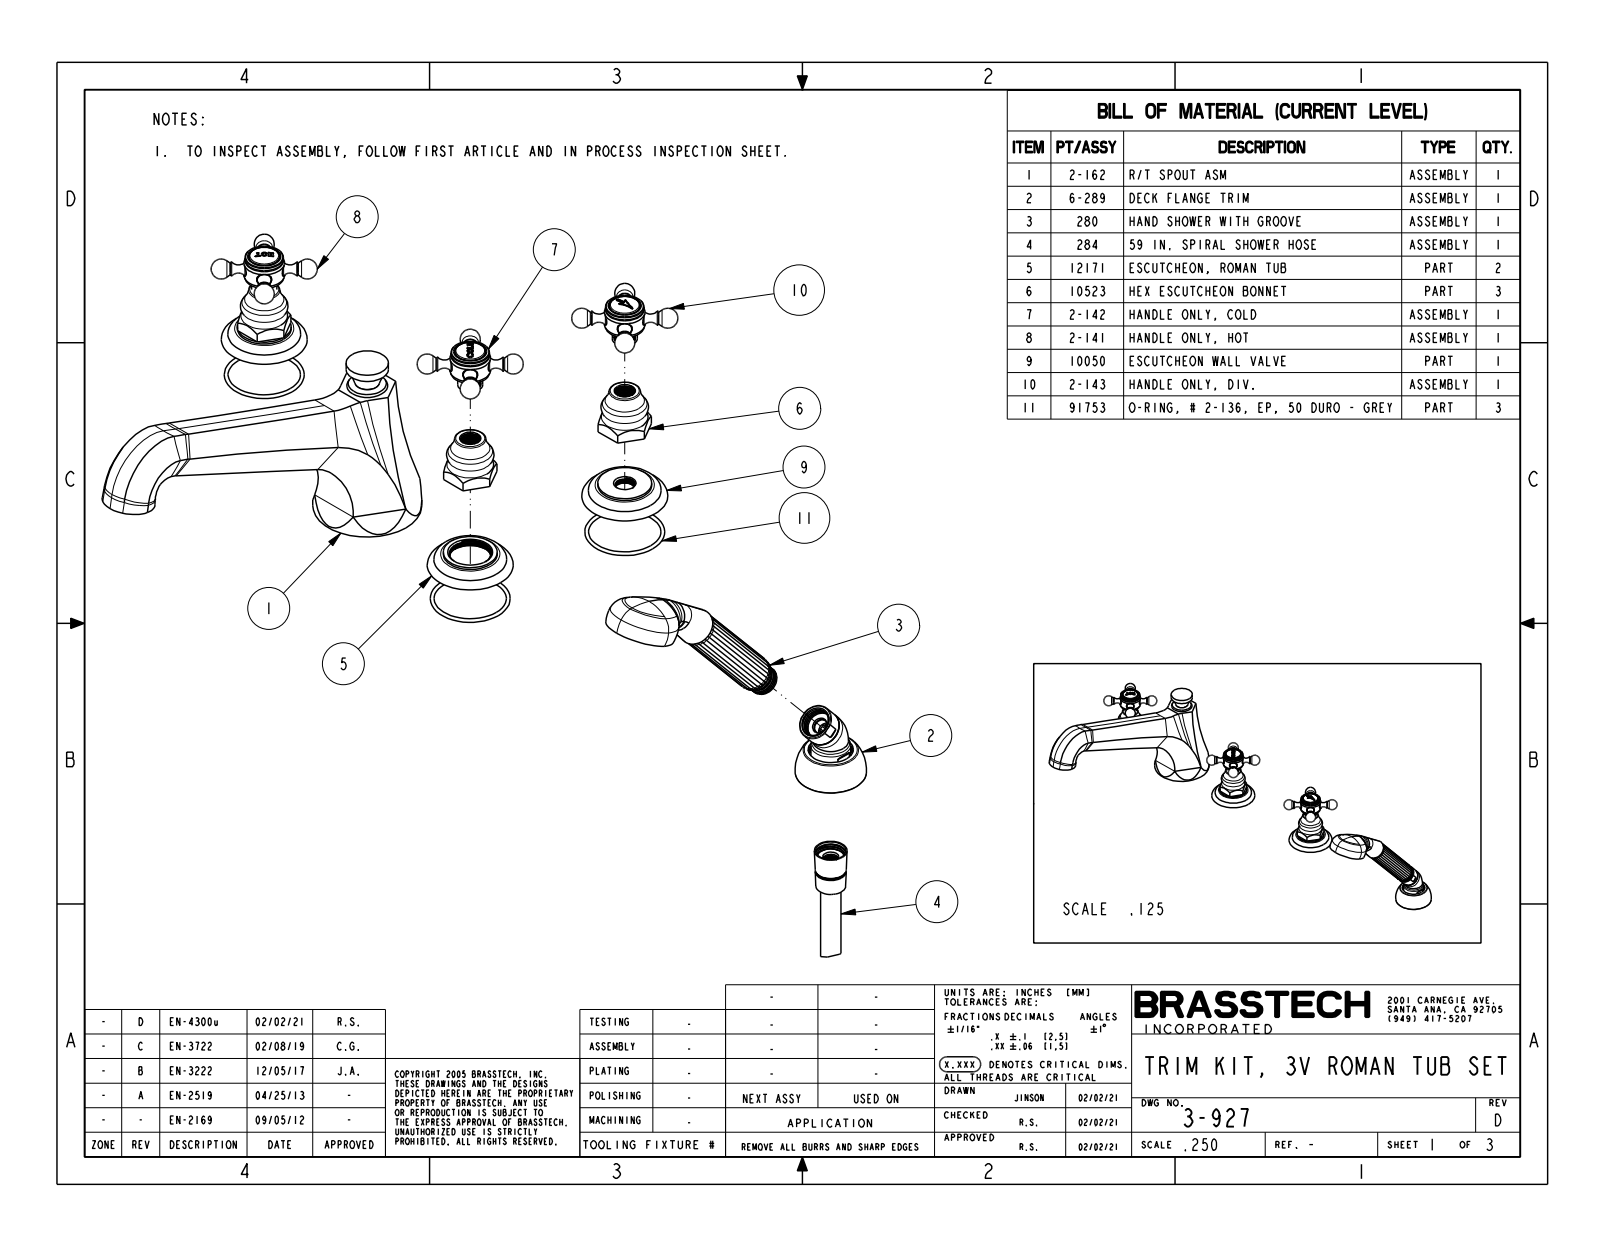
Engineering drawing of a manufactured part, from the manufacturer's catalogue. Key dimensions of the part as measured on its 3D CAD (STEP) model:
Part name (STEP PRODUCT): 3-927
STEP written by: CREO PARAMETRIC BY PTC INC, 2018400 (CONFIG_CONTROL_DESIGN)
Units: inches
Bodies: 7 solids, 1075 faces (195 planar, 281 cylindrical, 599 other)
Overall size (bounding box): 24.175 × 11.484 × 6.739
Volume: 54.92 in³ · Surface area: 201.2 in²
Round holes (diameter × count): ⌀0.046 ×52, ⌀0.41 ×6, ⌀0.855 ×3
Round bosses / shafts (diameter × count): ⌀0.392 ×10, ⌀1.482 ×3, ⌀1.055 ×3, ⌀0.687 ×3, ⌀2.99 ×1, ⌀1.823 ×1, ⌀1.65 ×1, ⌀1.26 ×1
Partial cylindrical surfaces — rounded edges, fillets, slot ends (radius × count): R0.006 ×7, R0.024 ×7, R0.05 ×6, R13 ×6, R0.03 ×5, R0.048 ×3, R0.015 ×2, R0.018 ×2
Main face-to-face distances: 1.313, 0.375, 5.196, 6.928, 12.124, 4.115, 3.74, 0.787, 0.412, 3.328
Hole centre spacings: 0.367, 0.185, 0.709, 0.543, 0.863, 1.002, 0.187, 1.369
